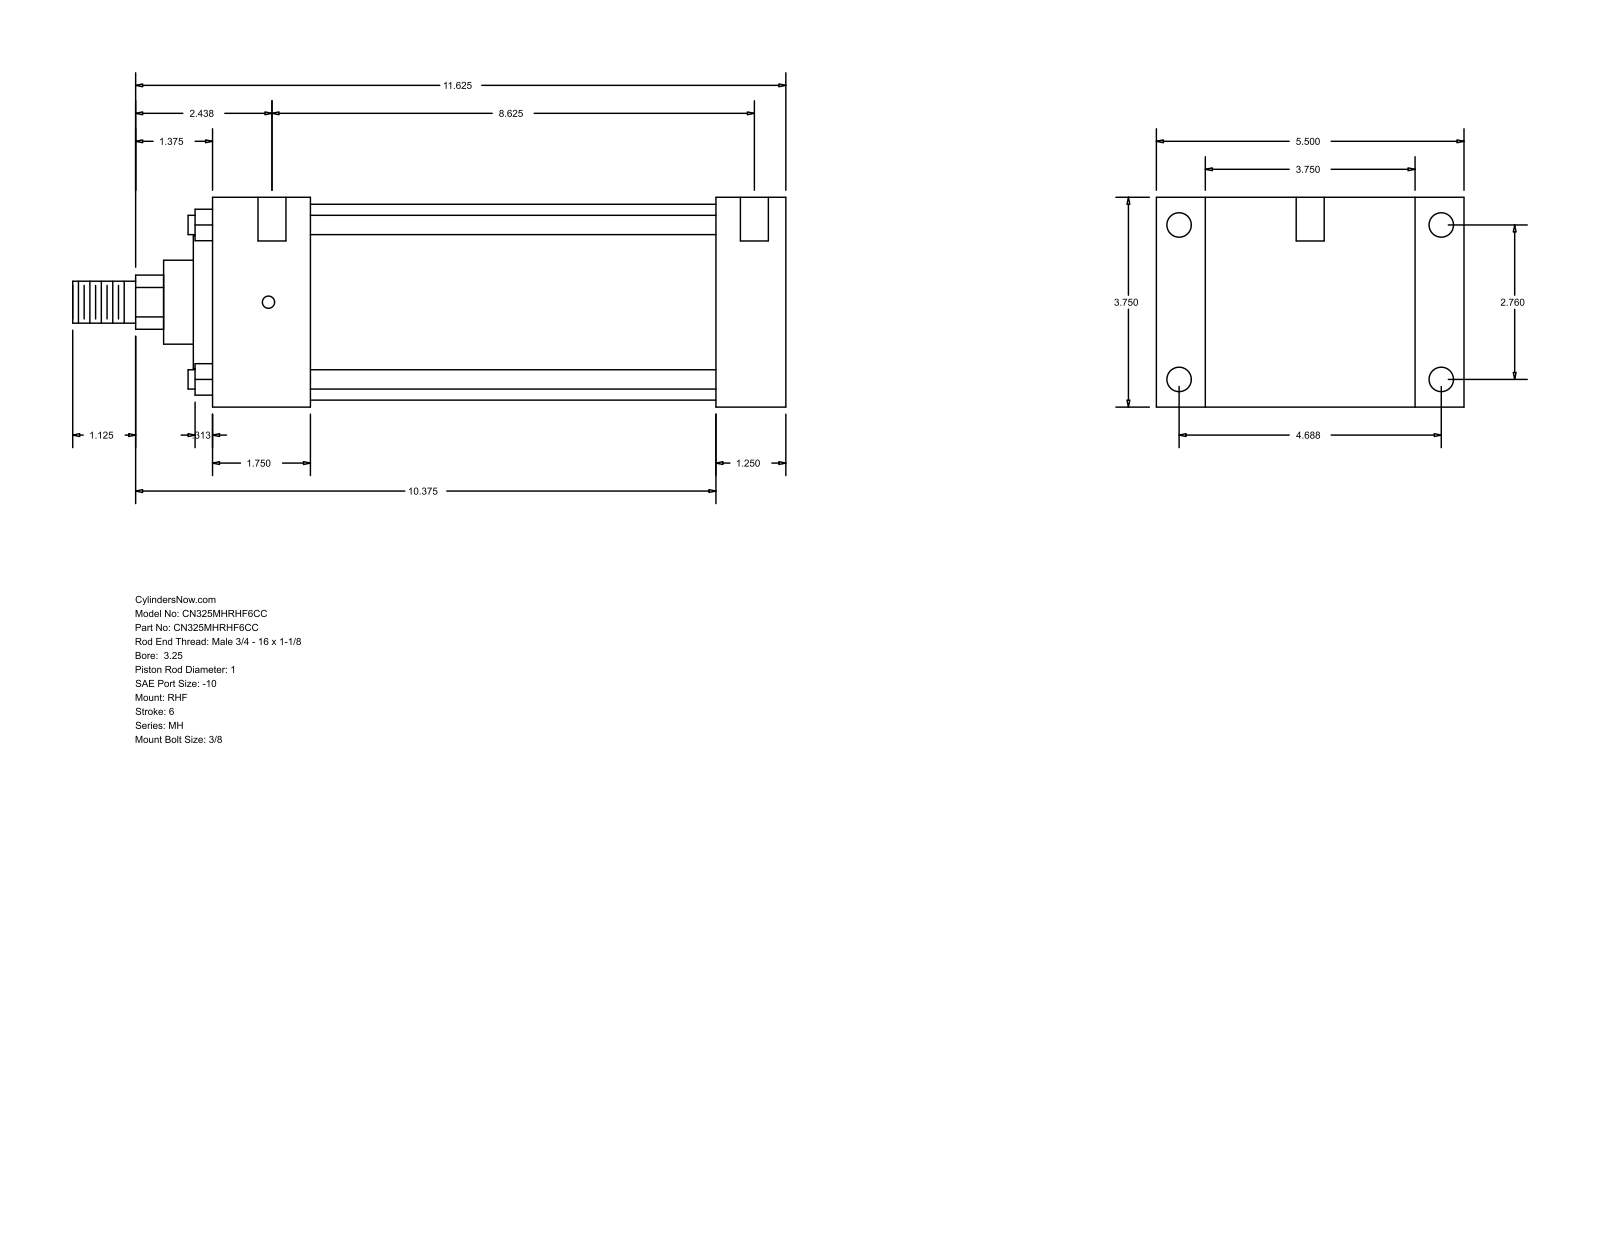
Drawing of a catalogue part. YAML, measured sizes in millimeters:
part_name: "MH_RHF__0325_1"
step_written_by: "GSSL Pune (CONFIG_CONTROL_DESIGN)"
units: millimeters
bodies: {solids: 0, faces: 90, planar: 61, cylindrical: 29, other: 0}
overall_size: [323.85, 139.7, 95.25]
round_holes:
  - {diameter: 5.56, count: 4}
  - {diameter: 11.13, count: 4}
  - {diameter: 12.7, count: 2}
round_bosses_or_shafts:
  - {diameter: 8.76, count: 4}
  - {diameter: 88.9, count: 1}
  - {diameter: 60.33, count: 1}
  - {diameter: 38.1, count: 1}
  - {diameter: 25.4, count: 1}
  - {diameter: 19.05, count: 1}
partial_cylinders:
  - {radius: 12.29, count: 1}
face_to_face_distances: [95.24, 31.75, 22.23, 117.47, 228.6, 260.35, 139.7, 44.46, 184.14, 215.89]
hole_center_spacings: [70.1, 119.06, 138.16, 225.42, 1.58, 4.76, 219.08, 220.66]
